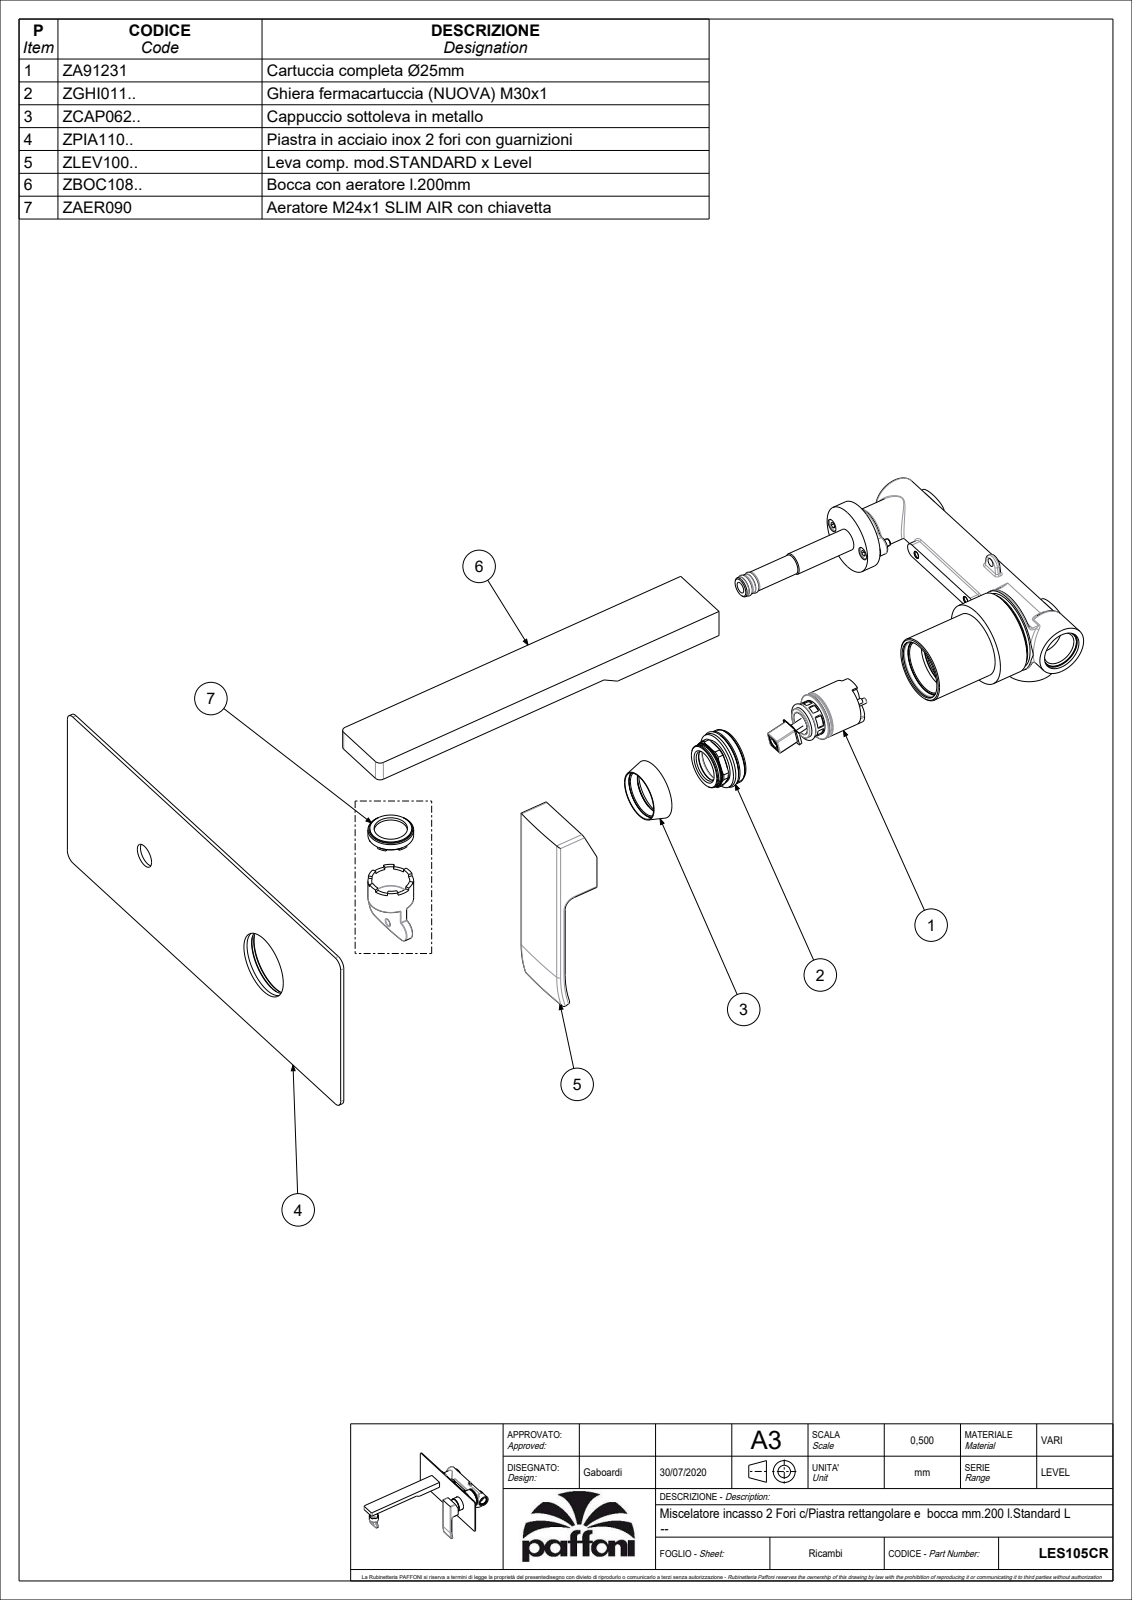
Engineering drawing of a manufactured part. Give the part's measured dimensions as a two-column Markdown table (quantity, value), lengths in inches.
| quantity | value |
| --- | --- |
| part name | LES105CR |
| STEP written by | CREO PARAMETRIC BY PTC INC, 2020044 (CONFIG_CONTROL_DESIGN) |
| units | inches |
| bodies | 2 solids, 740 faces (232 planar, 279 cylindrical, 229 other) |
| overall size | 9.843 × 8.661 × 5.565 |
| volume | 10.93 in³ |
| surface area | 165.7 in² |
| round holes (diameter × count) | 0.236 × 2, 0.118 × 1, 0.165 × 1, 0.217 × 1, 0.307 × 1, 0.433 × 1, 0.472 × 1, 0.512 × 1, 0.591 × 1, 0.657 × 1, 0.669 × 1, 0.689 × 1 |
| round bosses / shafts (diameter × count) | 1.386 × 1, 1.181 × 1, 1.091 × 1, 0.984 × 1, 0.937 × 1, 0.886 × 1, 0.748 × 1, 0.728 × 1 |
| partial cylindrical surfaces (radius × count) | 0.02 × 56, 0.079 × 16, 0.039 × 11, 0.059 × 8, 0.197 × 4, 0.083 × 2, 0.098 × 2, 0.118 × 2 |
| main face-to-face distances | 0.079, 0.453, 1.378, 0.197, 0.65, 4.291, 5.669, 2.913, 1.644, 2.293 |
| hole center spacings | 4.291, 7.94 |
